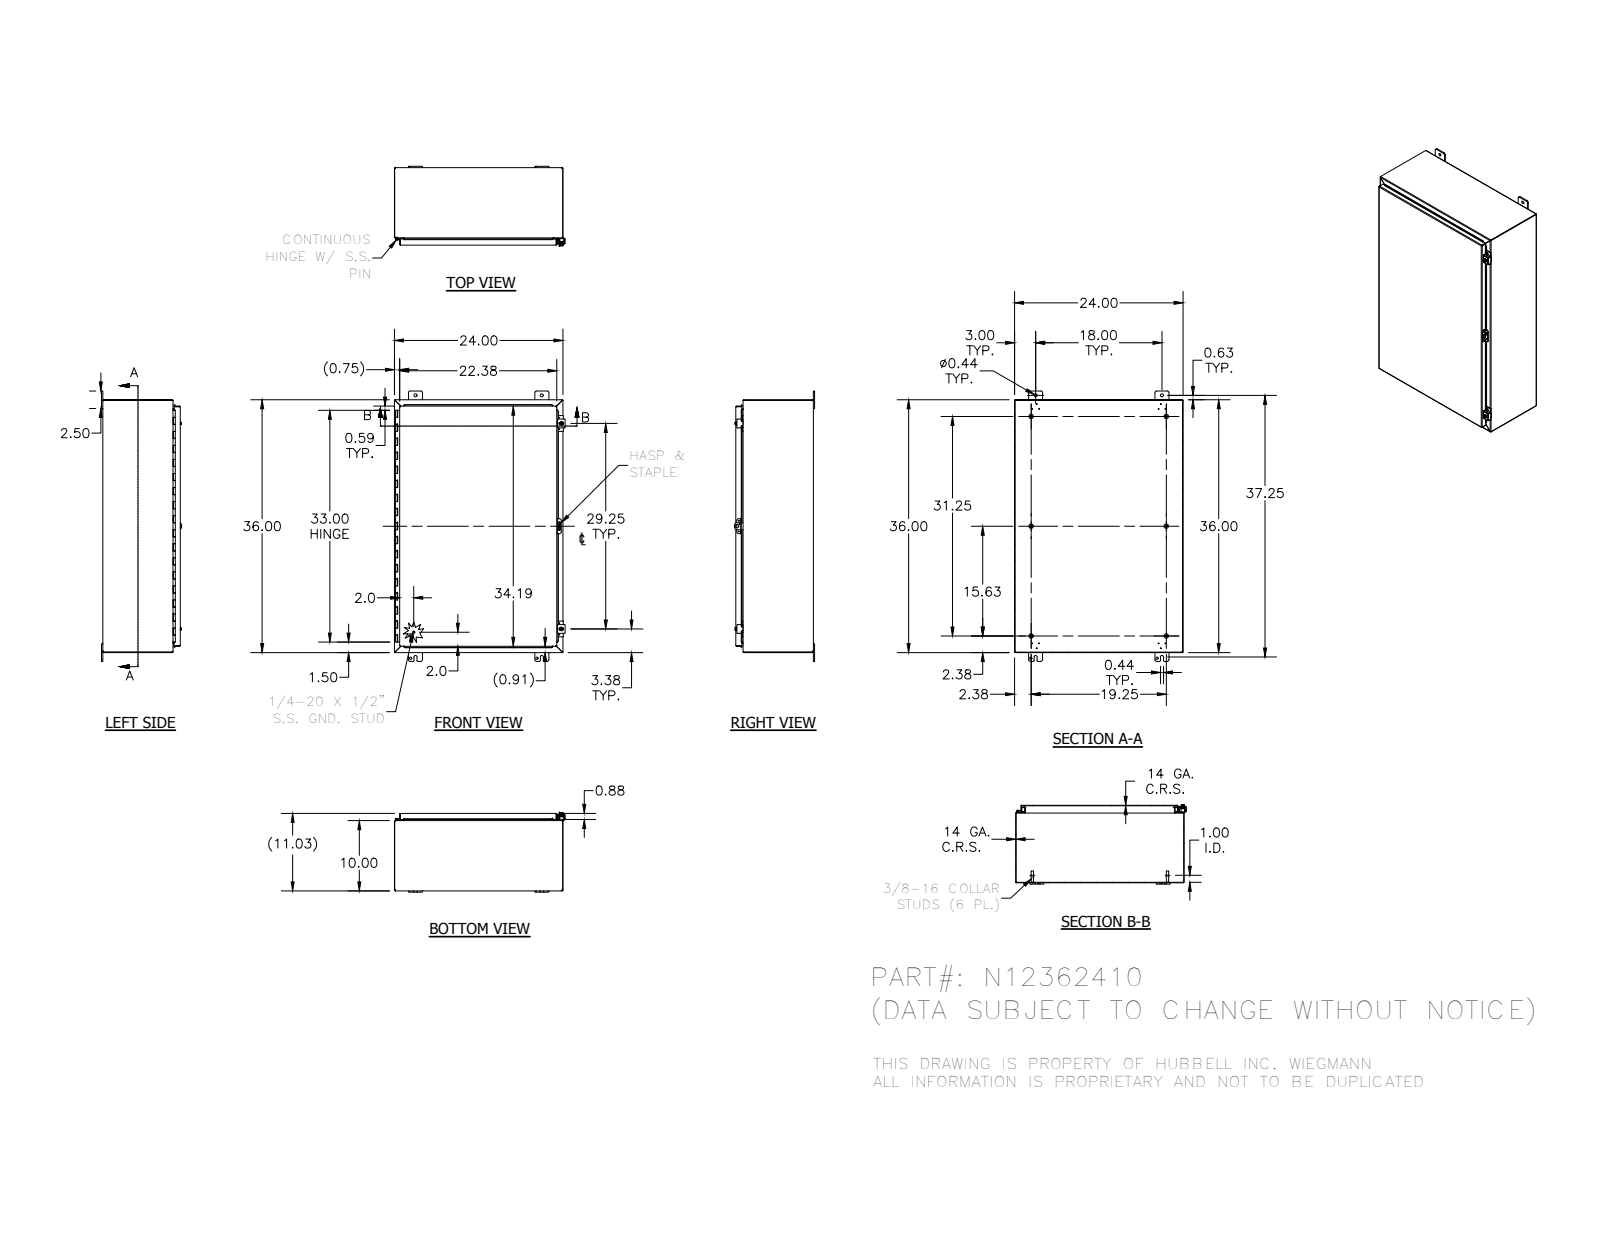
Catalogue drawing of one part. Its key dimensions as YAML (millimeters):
part_name: "N12362410; 34840; 38420; N12362410BKP (+8 more)"
step_written_by: "Autodesk Inventor 2012 (AUTOMOTIVE_DESIGN)"
units: millimeters
bodies: {solids: 29, faces: 1100, planar: 607, cylindrical: 374, other: 119}
overall_size: [977.9, 617.5, 289.8]
volume: 4205000
surface_area: 4356000
round_holes:
  - {diameter: 3, count: 12}
  - {diameter: 2.8, count: 7}
  - {diameter: 8, count: 4}
  - {diameter: 11.1, count: 4}
  - {diameter: 5.4, count: 2}
  - {diameter: 7.1, count: 2}
  - {diameter: 7.6, count: 2}
  - {diameter: 3.2, count: 1}
  - {diameter: 4, count: 1}
  - {diameter: 12.7, count: 1}
round_bosses_or_shafts:
  - {diameter: 15.9, count: 6}
  - {diameter: 8.4, count: 6}
  - {diameter: 6.4, count: 4}
  - {diameter: 13.2, count: 2}
  - {diameter: 12.7, count: 2}
  - {diameter: 8.9, count: 2}
  - {diameter: 2.9, count: 2}
  - {diameter: 8.6, count: 1}
partial_cylinders:
  - {radius: 0.8, count: 27}
  - {radius: 1.6, count: 25}
  - {radius: 3.2, count: 25}
  - {radius: 6.4, count: 25}
  - {radius: 0.8, count: 23}
  - {radius: 2.7, count: 23}
  - {radius: 1.8, count: 8}
  - {radius: 2.5, count: 4}
face_to_face_distances: [1.9, 278.4, 276.5, 280.2, 607.7, 912.5, 605.8, 609.6, 252.1, 26.2]
hole_center_spacings: [457.2, 19.3, 21.3, 23.9, 24.6, 40.5, 50.7, 441.2]
